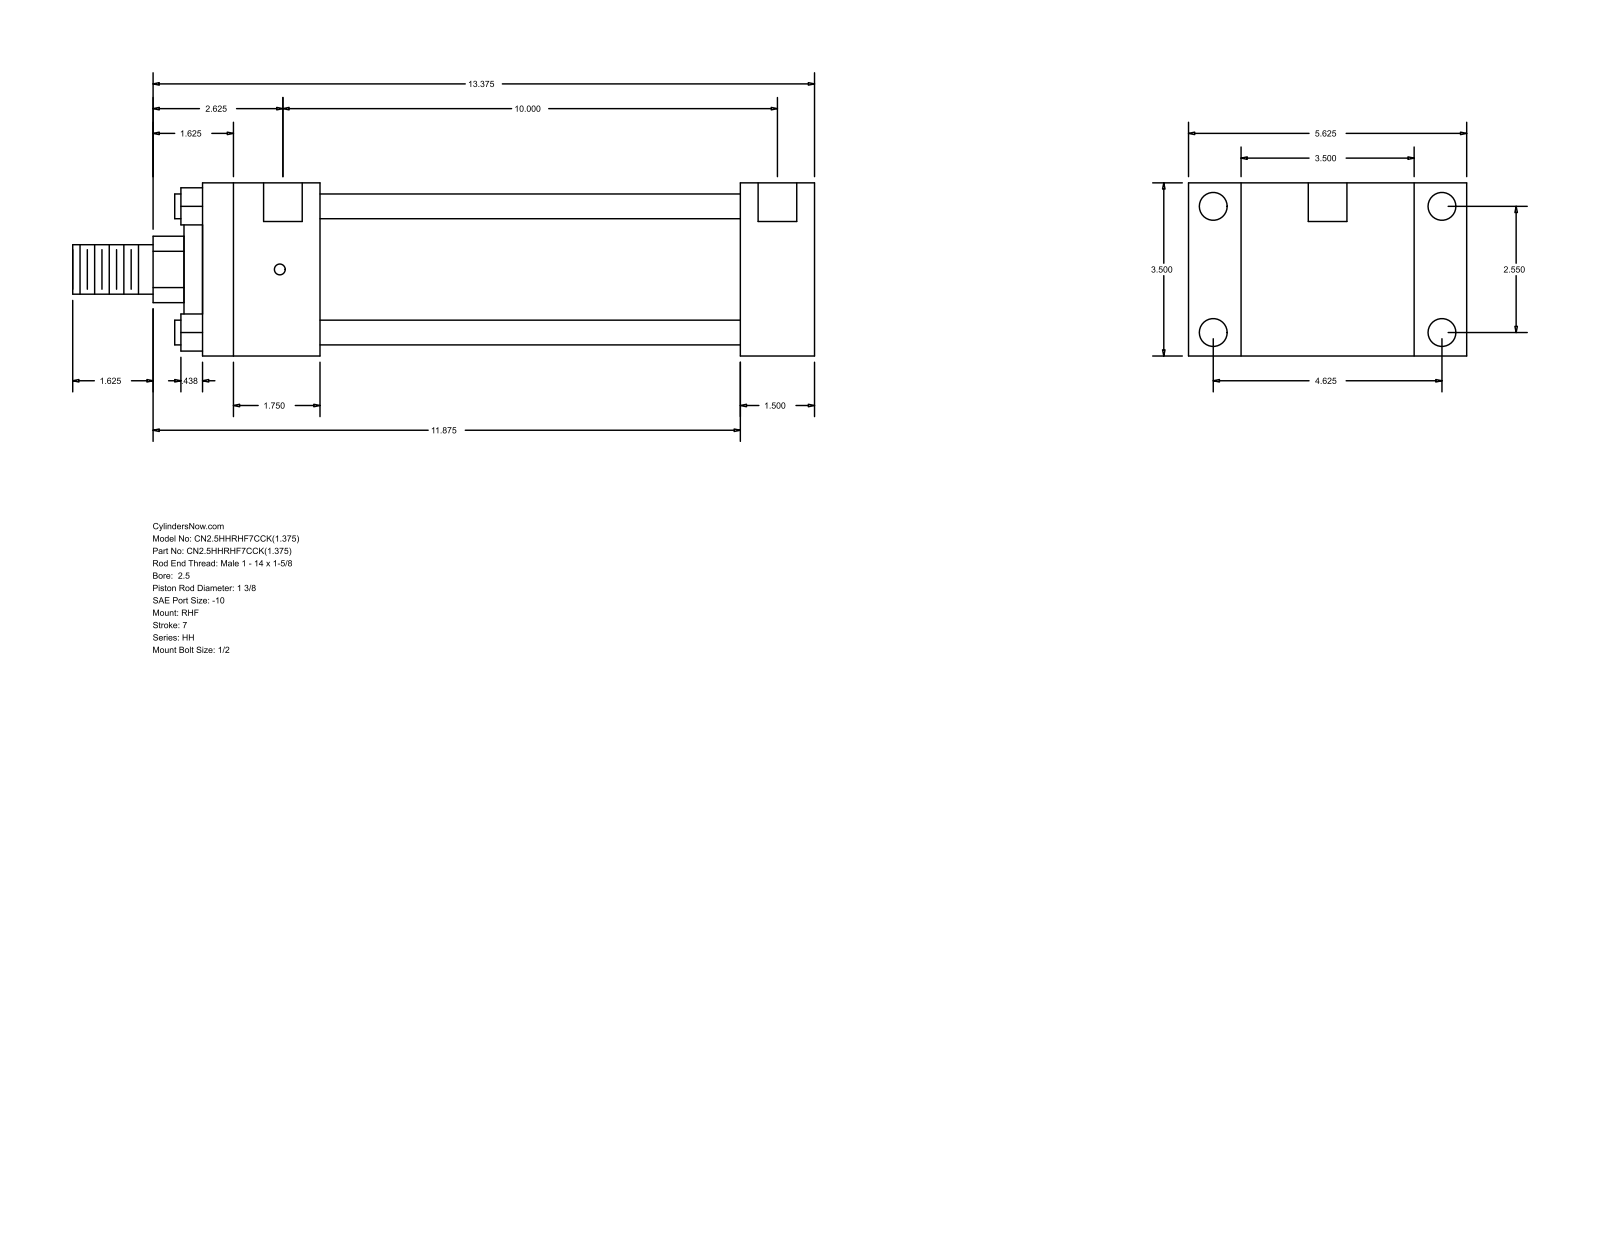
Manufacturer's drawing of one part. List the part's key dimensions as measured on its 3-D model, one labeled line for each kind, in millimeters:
Part name (STEP PRODUCT): HH_RHF__0250_1.375
STEP written by: GSSL Pune (CONFIG_CONTROL_DESIGN)
Units: millimetres
Bodies: 0 solids, 88 faces (60 planar, 28 cylindrical, 0 other)
Overall size (bounding box): 381 × 142.88 × 88.9
Round holes (diameter × count): ⌀5.56 ×4, ⌀14.3 ×4, ⌀19.84 ×2
Round bosses / shafts (diameter × count): ⌀12.7 ×4, ⌀73.03 ×1, ⌀50.8 ×1, ⌀34.92 ×1, ⌀25.4 ×1
Partial cylindrical surfaces — rounded edges, fillets, slot ends (radius × count): R17.06 ×1
Main face-to-face distances: 88.9, 38.11, 26.99, 115.89, 276.22, 314.33, 142.88, 60.32, 215.9, 254.01
Hole centre spacings: 1.58, 64.76, 117.48, 134.15, 255.59, 257.17, 254.01
